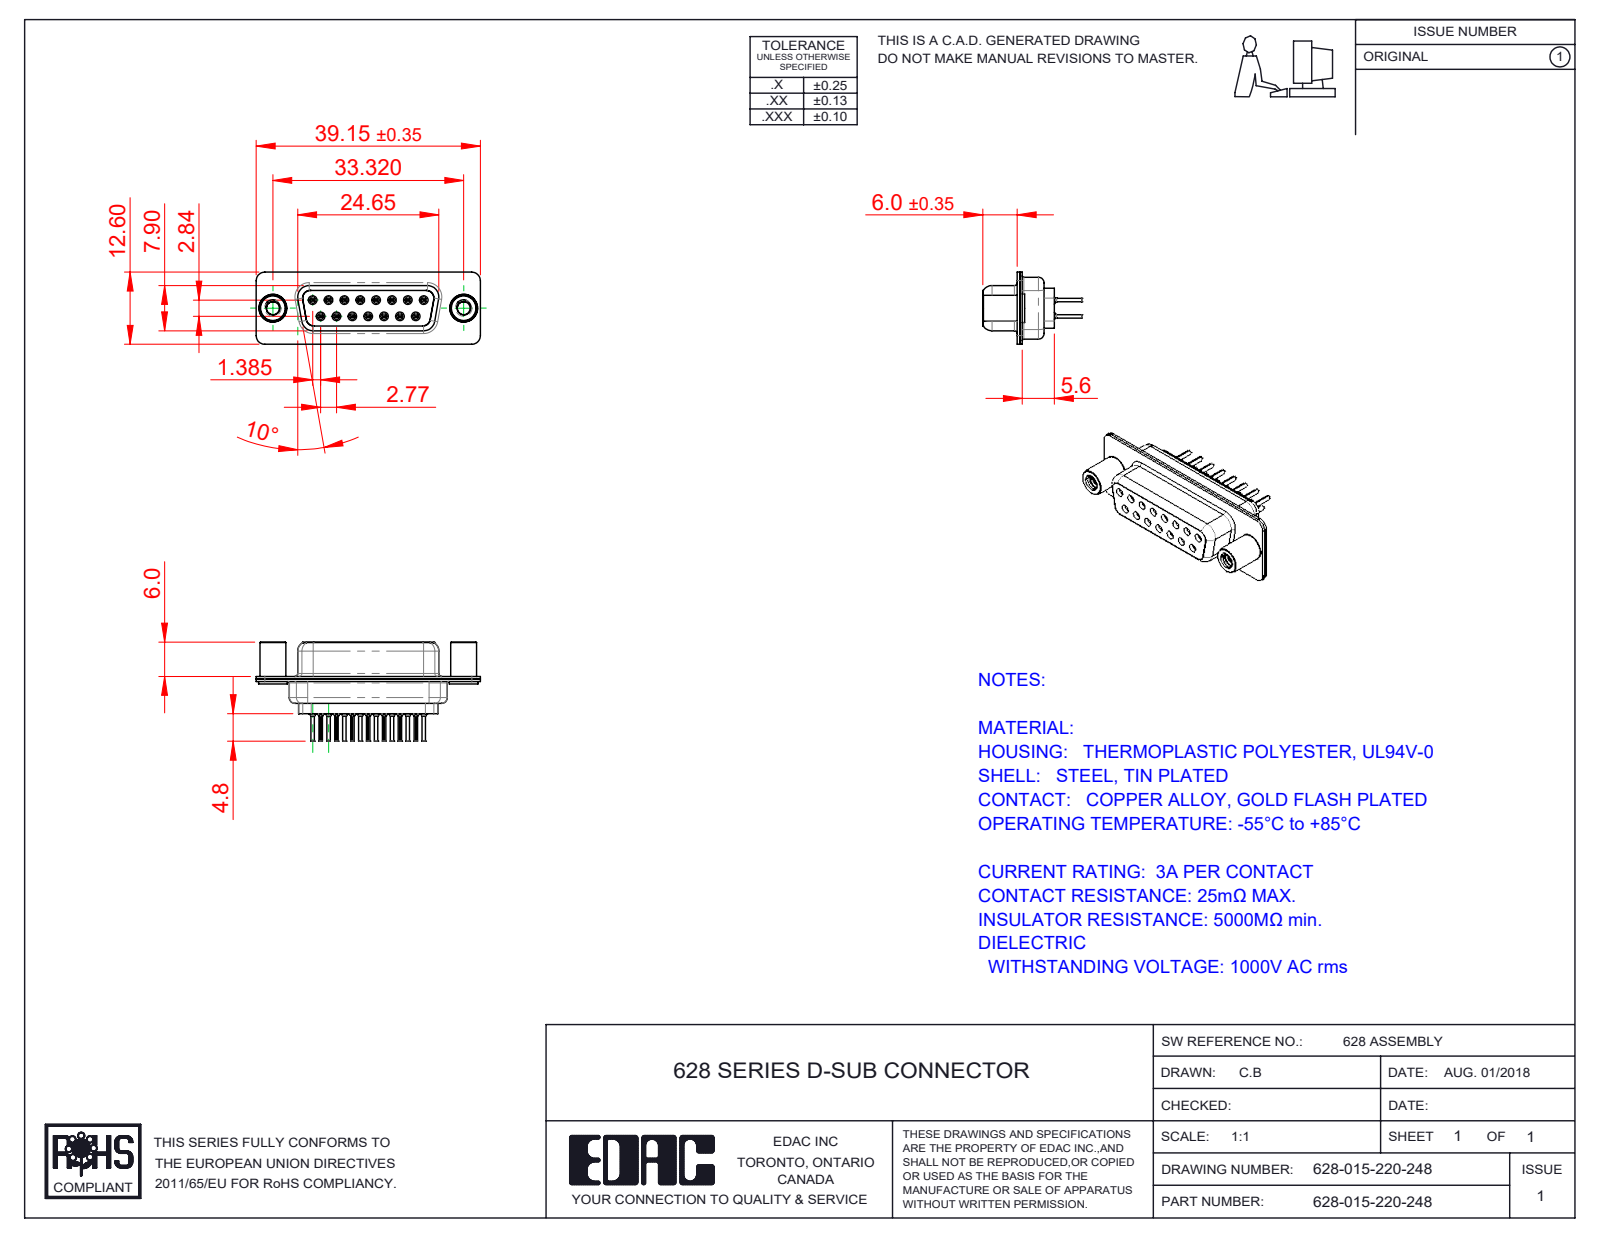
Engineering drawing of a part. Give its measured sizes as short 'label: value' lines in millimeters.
name: 628 Shell Rear_15 Contacts; 628 Contact Row 1_20L; 628 4-40 Threaded Standoff; 628-015-220-248 (+3 more)
written by: SolidWorks 2020 (CONFIG_CONTROL_DESIGN)
unit: mm
bodies: 20 solids, 2218 faces (534 planar, 660 cylindrical, 1024 other)
size: 39.15 × 17.3 × 12.6
volume: 2 607 mm³; area: 6 525 mm²
holes: 15× ⌀0.2, 15× ⌀0.8, 15× ⌀0.9, 15× ⌀1.1, 15× ⌀1.6, 8× ⌀1.7, 2× ⌀2.26, 2× ⌀4, 2× ⌀4.05, 2× ⌀4.85
bosses: 15× ⌀2, 15× ⌀1.5, 15× ⌀1.2, 15× ⌀0.6, 2× ⌀5, 2× ⌀4.95, 2× ⌀4.8, 2× ⌀4.5
rounds: 30× R0.1, 18× R1.5, 15× R0.28, 12× R2, 8× R1.35, 4× R0.25, 4× R0.5, 4× R0.6
face distances: 0.45, 0.4, 0.9, 6.6, 1.9, 8.5, 0.85, 1.4, 1.8, 7.05
hole spacings: 3.16, 2.77, 5.54, 8.31, 11.08, 5.03, 5.04, 7.48
